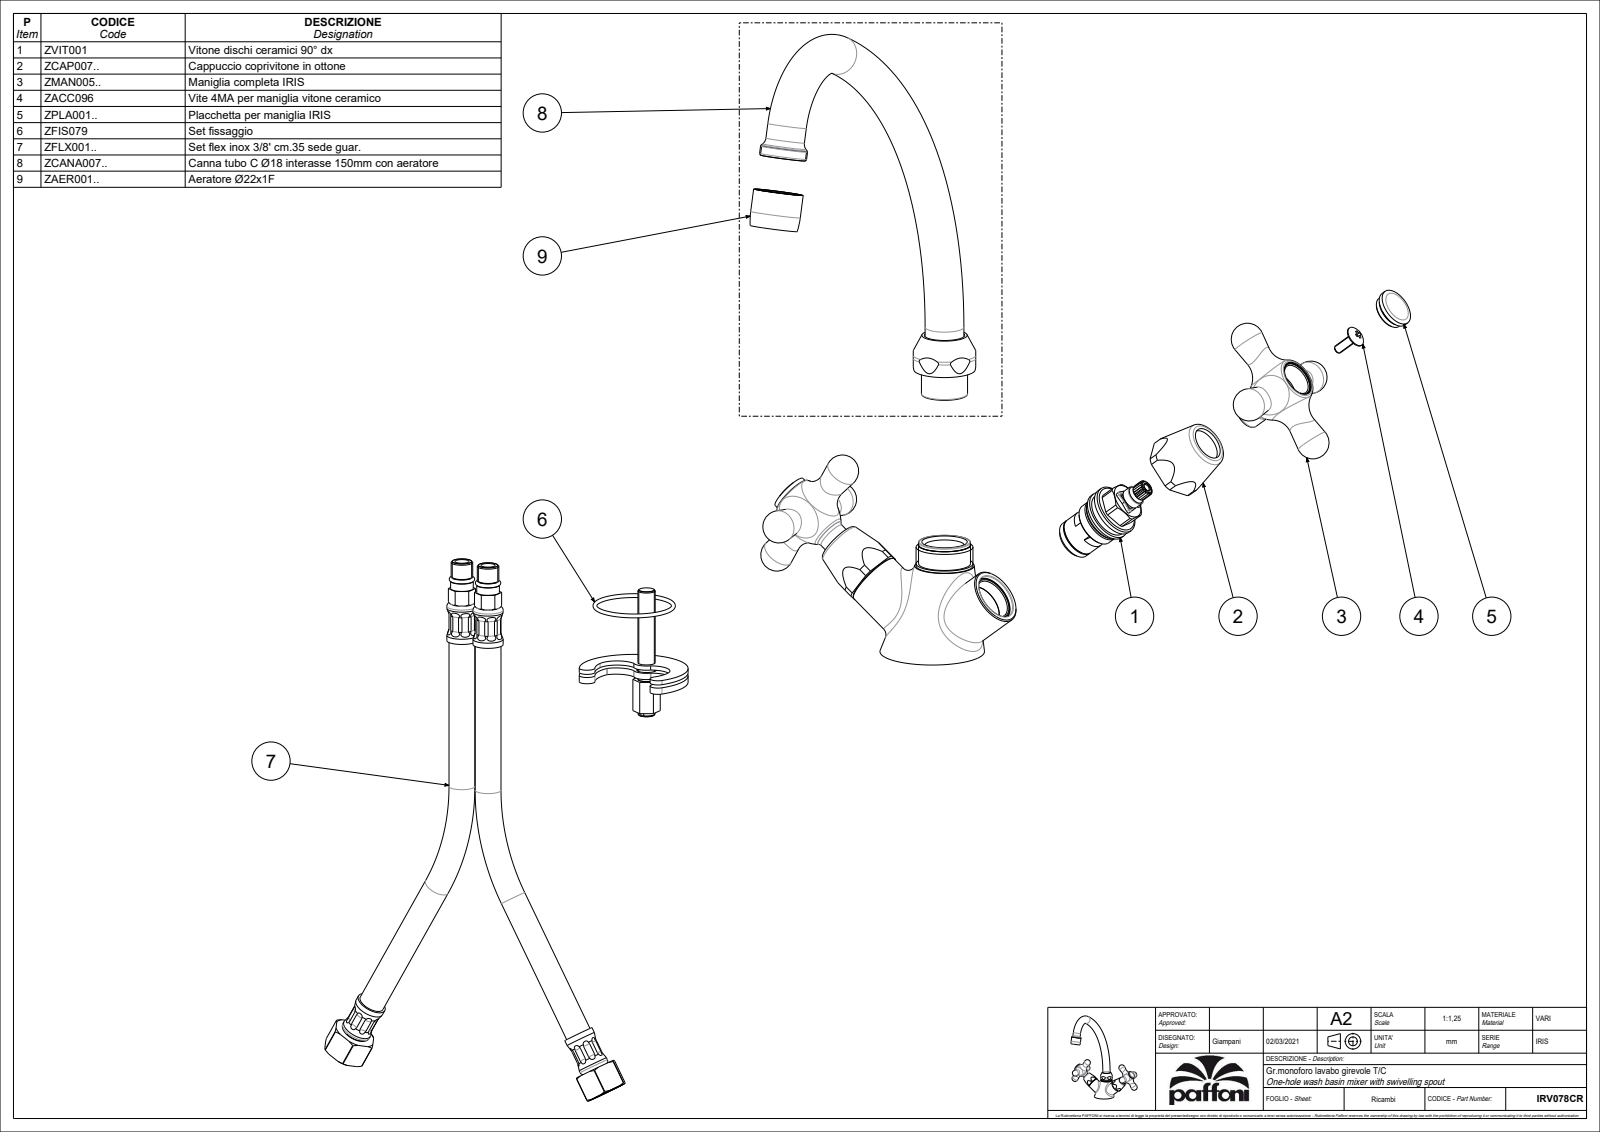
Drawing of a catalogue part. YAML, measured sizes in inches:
part_name: "IRV078CR"
step_written_by: "CREO PARAMETRIC BY PTC INC, 2020044 (CONFIG_CONTROL_DESIGN)"
units: inches
bodies: {solids: 1, faces: 462, planar: 136, cylindrical: 98, other: 228}
overall_size: [8.996, 7.513, 7.243]
volume: 11.51
surface_area: 89.59
round_holes:
  - {diameter: 0.354, count: 4}
  - {diameter: 0.315, count: 2}
  - {diameter: 0.433, count: 2}
  - {diameter: 0.618, count: 2}
  - {diameter: 0.709, count: 2}
  - {diameter: 0.748, count: 2}
  - {diameter: 0.827, count: 2}
  - {diameter: 0.846, count: 2}
  - {diameter: 0.906, count: 2}
  - {diameter: 0.236, count: 1}
  - {diameter: 0.268, count: 1}
  - {diameter: 0.472, count: 1}
round_bosses_or_shafts:
  - {diameter: 0.709, count: 4}
  - {diameter: 1.035, count: 2}
  - {diameter: 0.531, count: 2}
  - {diameter: 1.339, count: 1}
  - {diameter: 1.039, count: 1}
  - {diameter: 0.913, count: 1}
  - {diameter: 0.866, count: 1}
  - {diameter: 0.705, count: 1}
partial_cylinders:
  - {radius: 0.571, count: 2}
face_to_face_distances: [1.043, 0.866, 0.945, 1.681, 0.051, 1.63, 1.811, 0.079, 1.043, 1.807]
hole_center_spacings: [0.276, 0.527, 0.547, 0.024, 0.449, 0.472, 0.551]
